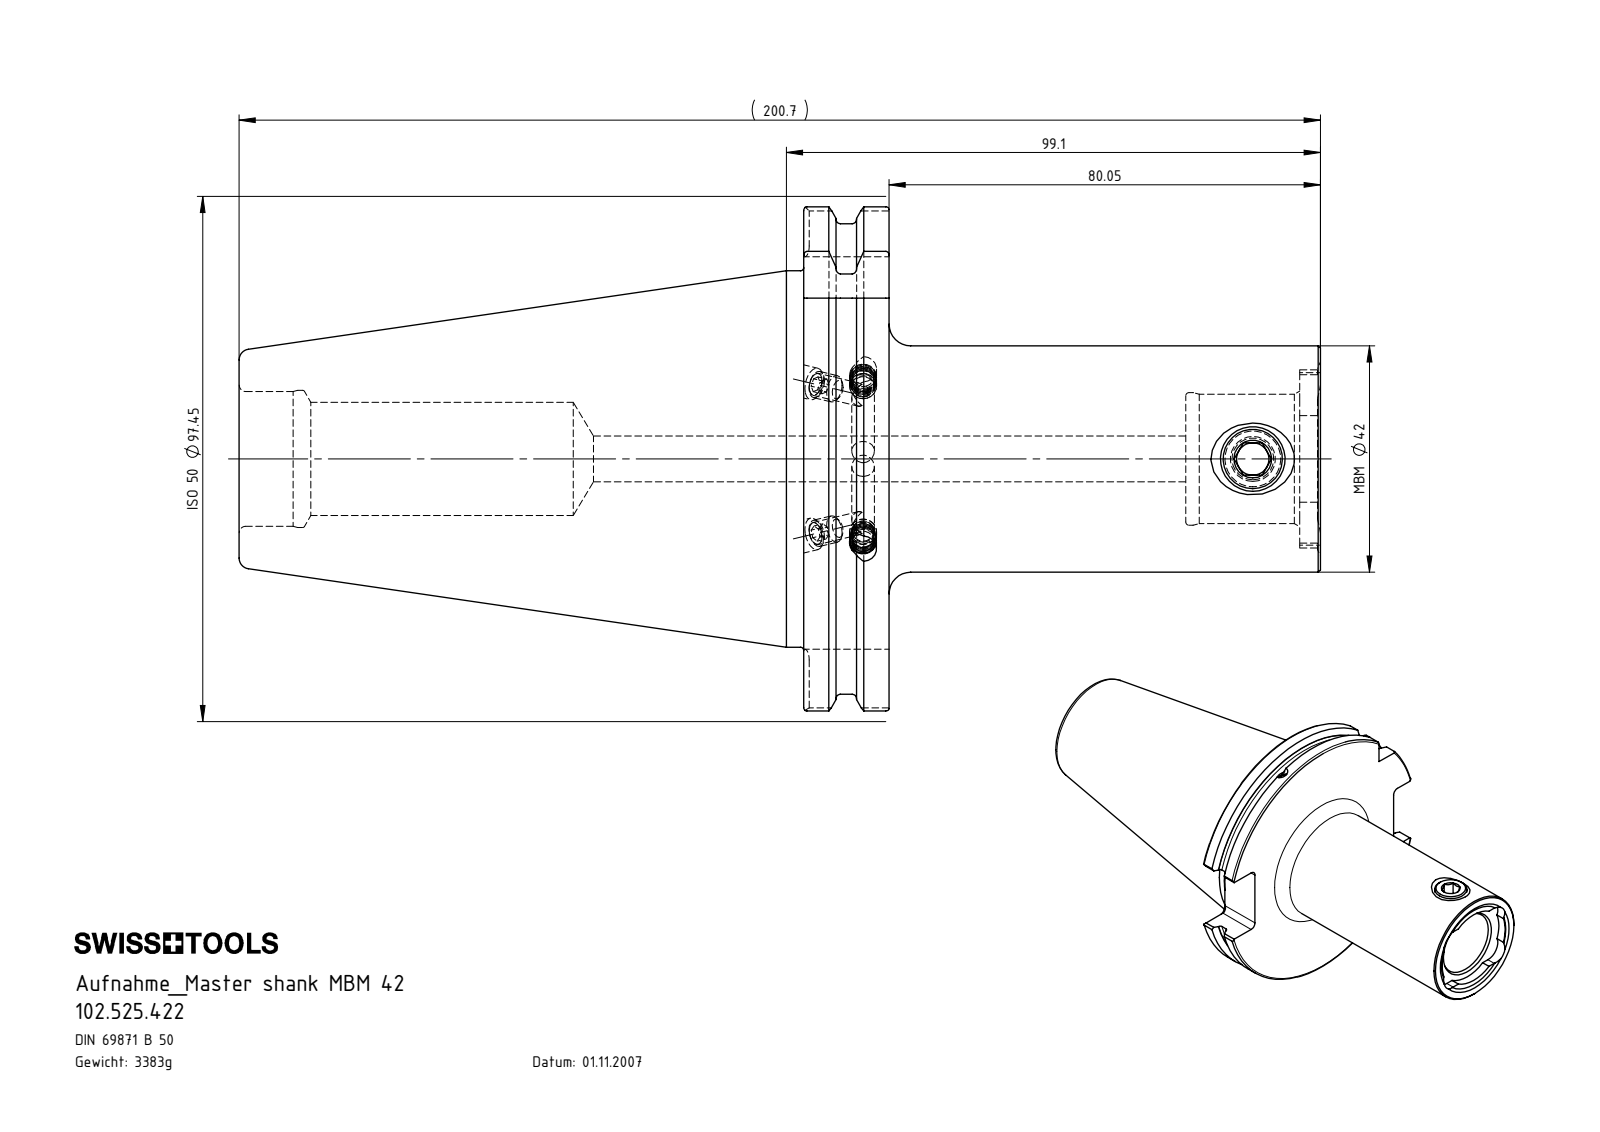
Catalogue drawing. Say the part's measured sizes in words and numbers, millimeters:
The part is named "102.525.422; KVT_MB_600_050; ISO 4026 - M5 x 5_PreviewCfg; MB4-ER1.001.013_A (+1 more)". Its 3-D file was written by "SolidWorks 2017 (CONFIG_CONTROL_DESIGN)". It is 8 solids with 300 faces: 79 planar, 82 cylindrical and 139 other. Overall it measures 200.7 by 97.45 by 93.51 millimeters. Its volume is 430 996 cubic millimeters and its surface area 57 682 square millimeters. Round holes: 3 of diameter 4.2, 3 of diameter 6, 2 of diameter 4, 1 of diameter 5, 1 of diameter 8.5, 1 of diameter 11, 1 of diameter 21, 1 of diameter 24, 1 of diameter 24.6, 1 of diameter 25, 1 of diameter 25.45. Round bosses or shafts: 3 of diameter 5, 1 of diameter 91, 1 of diameter 69.85, 1 of diameter 42, 1 of diameter 12. Partial cylindrical surfaces (rounded edges, fillets, slot ends): 8 of radius 2, 4 of radius 5.2, 1 of radius 14.9, 1 of radius 16.52, 1 of radius 48.73. The main face-to-face distances are 15.85, 104.8, 120.65, 21.15, 175.7, 70.9, 55.05, 72.8, 196.85, 92.05.
